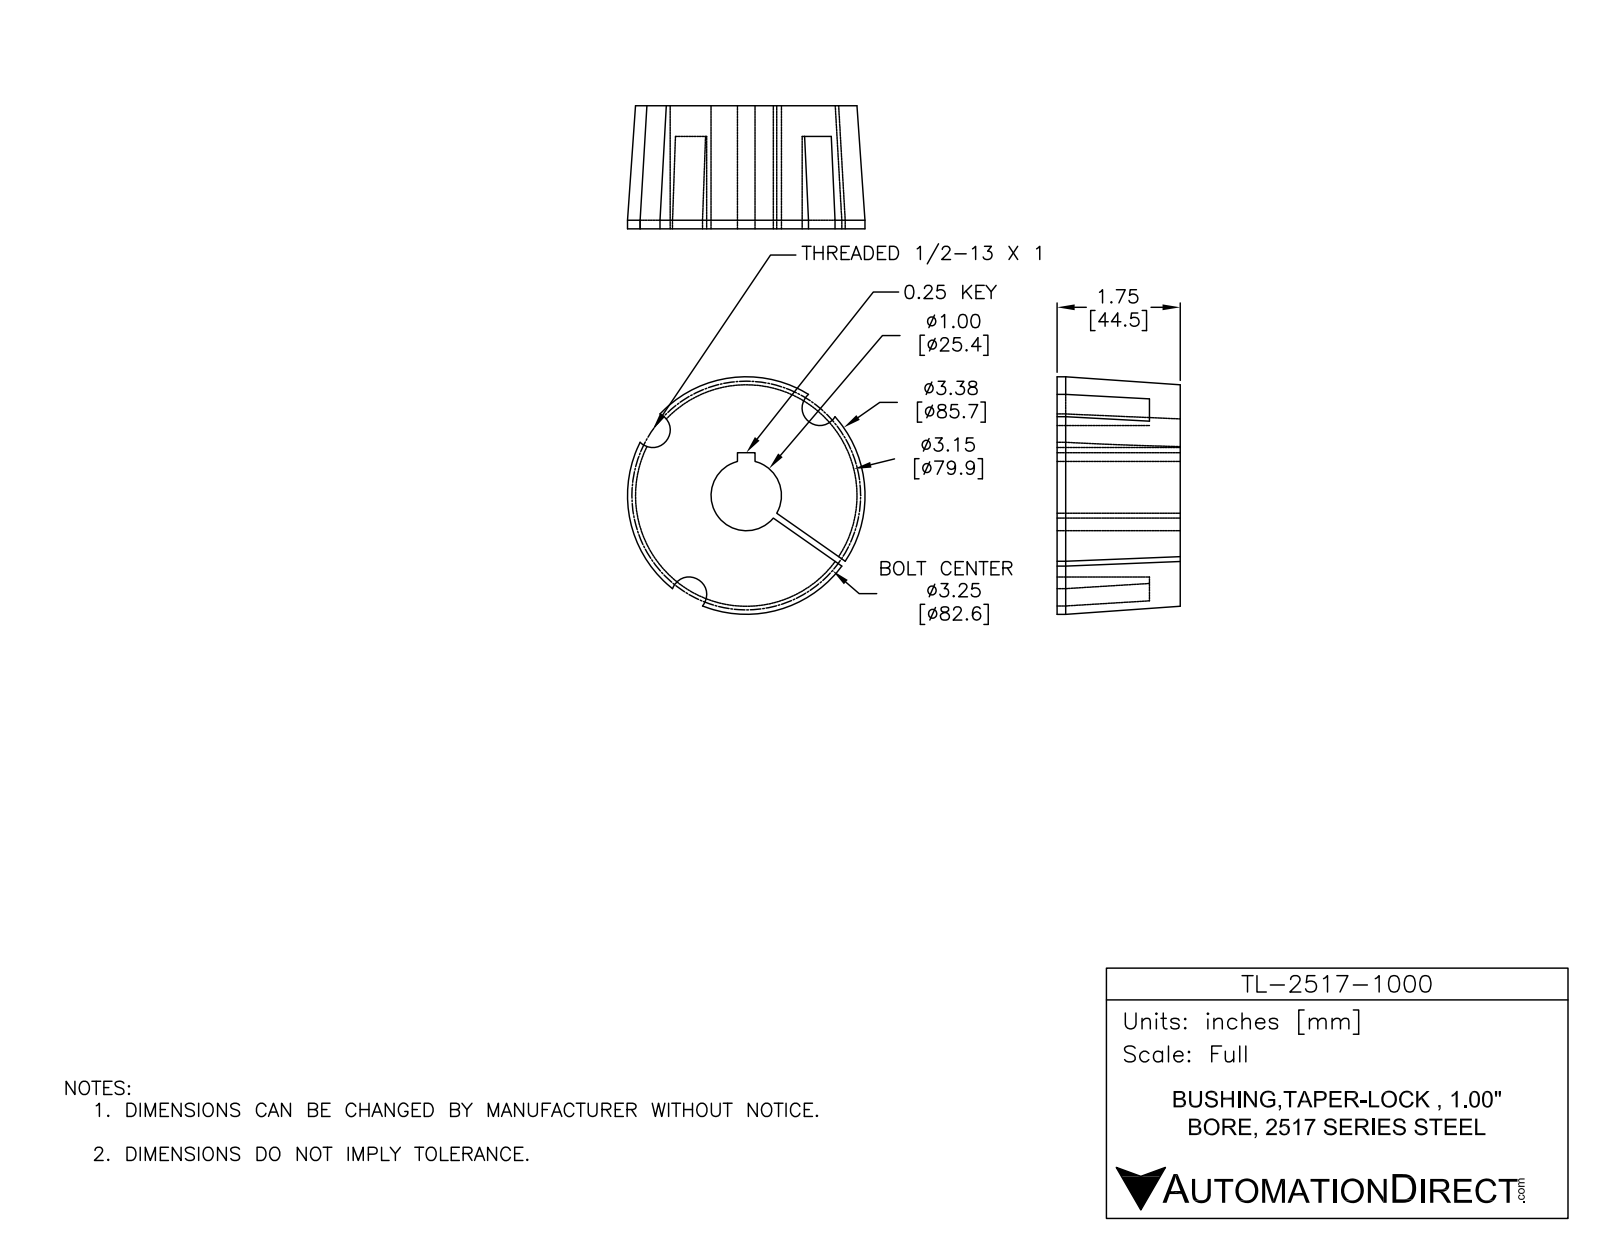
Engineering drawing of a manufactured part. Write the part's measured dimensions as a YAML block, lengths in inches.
part_name: "TL-2517-1000"
step_written_by: "SolidWorks 2014 (AUTOMOTIVE_DESIGN)"
units: inches
bodies: {solids: 1, faces: 24, planar: 9, cylindrical: 12, other: 3}
overall_size: [3.375, 3.375, 1.75]
volume: 12.65
surface_area: 43.5
round_holes:
  - {diameter: 1, count: 1}
round_bosses_or_shafts:
  - {diameter: 3.375, count: 1}
partial_cylinders:
  - {radius: 0.25, count: 3}
face_to_face_distances: [1.75, 0.085, 0.25, 0.437, 1.313]
